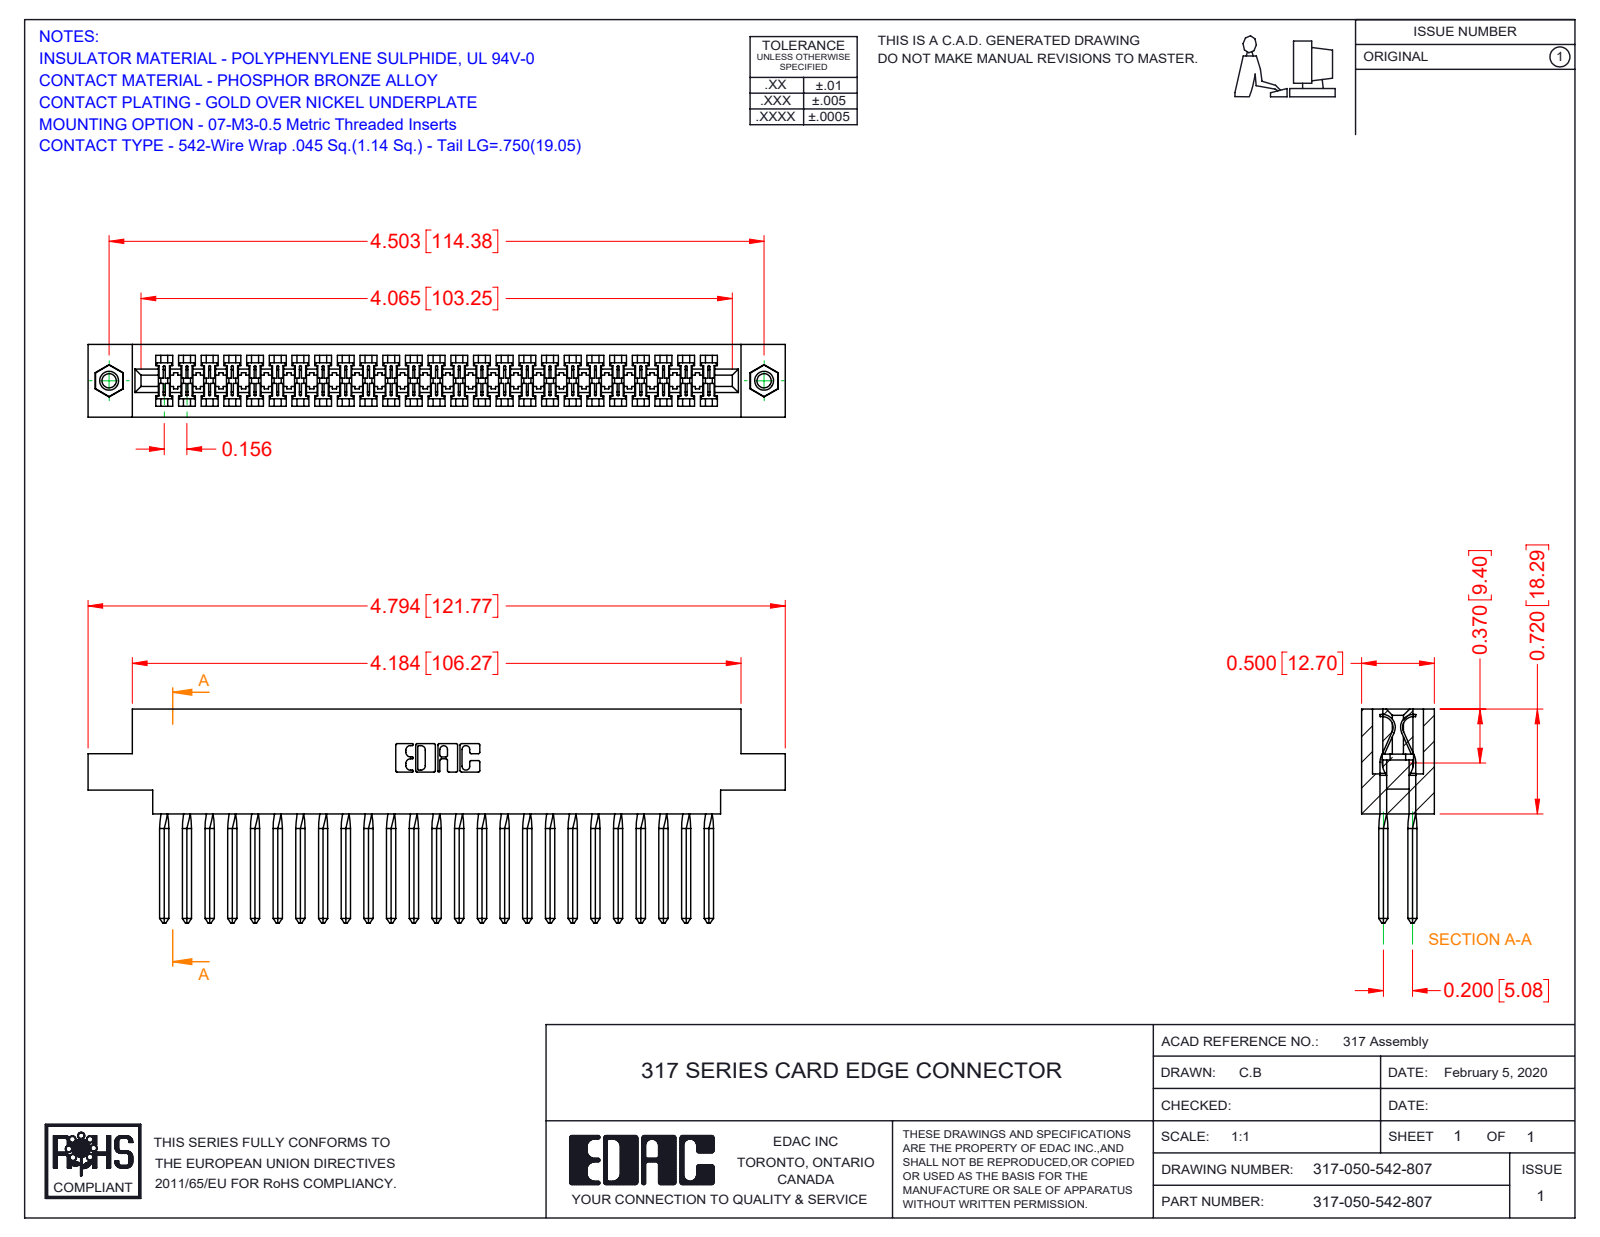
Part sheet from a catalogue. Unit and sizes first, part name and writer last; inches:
Units: inches
Overall size (bounding box): 4.794 × 1.47 × 0.5
Round holes (diameter × count): ⌀0.098 ×2, ⌀0.125 ×2, ⌀0.156 ×2
Round bosses / shafts (diameter × count): ⌀0.155 ×2
Partial cylindrical surfaces — rounded edges, fillets, slot ends (radius × count): R0.006 ×100, R0.01 ×22, R0.007 ×6, R0.031 ×6, R0.026 ×3, R0.074 ×2, R0.089 ×2, R0.1 ×2
Main face-to-face distances: 0.5, 0.075, 0.425, 0.35, 0.2, 0.11, 0.116, 0.136, 0.046, 0.72
Hole centre spacings: 4.503
Volume: 1.183 in³ · Surface area: 41 in²
Bodies: 53 solids, 3012 faces (2390 planar, 406 cylindrical, 216 other)
Part name (STEP PRODUCT): 317-290-003_542; 345-250-001_345-250-005-103; 317 Part_.156 Dia - TI; 317-050-542-807
STEP written by: SolidWorks 2016 (CONFIG_CONTROL_DESIGN)
